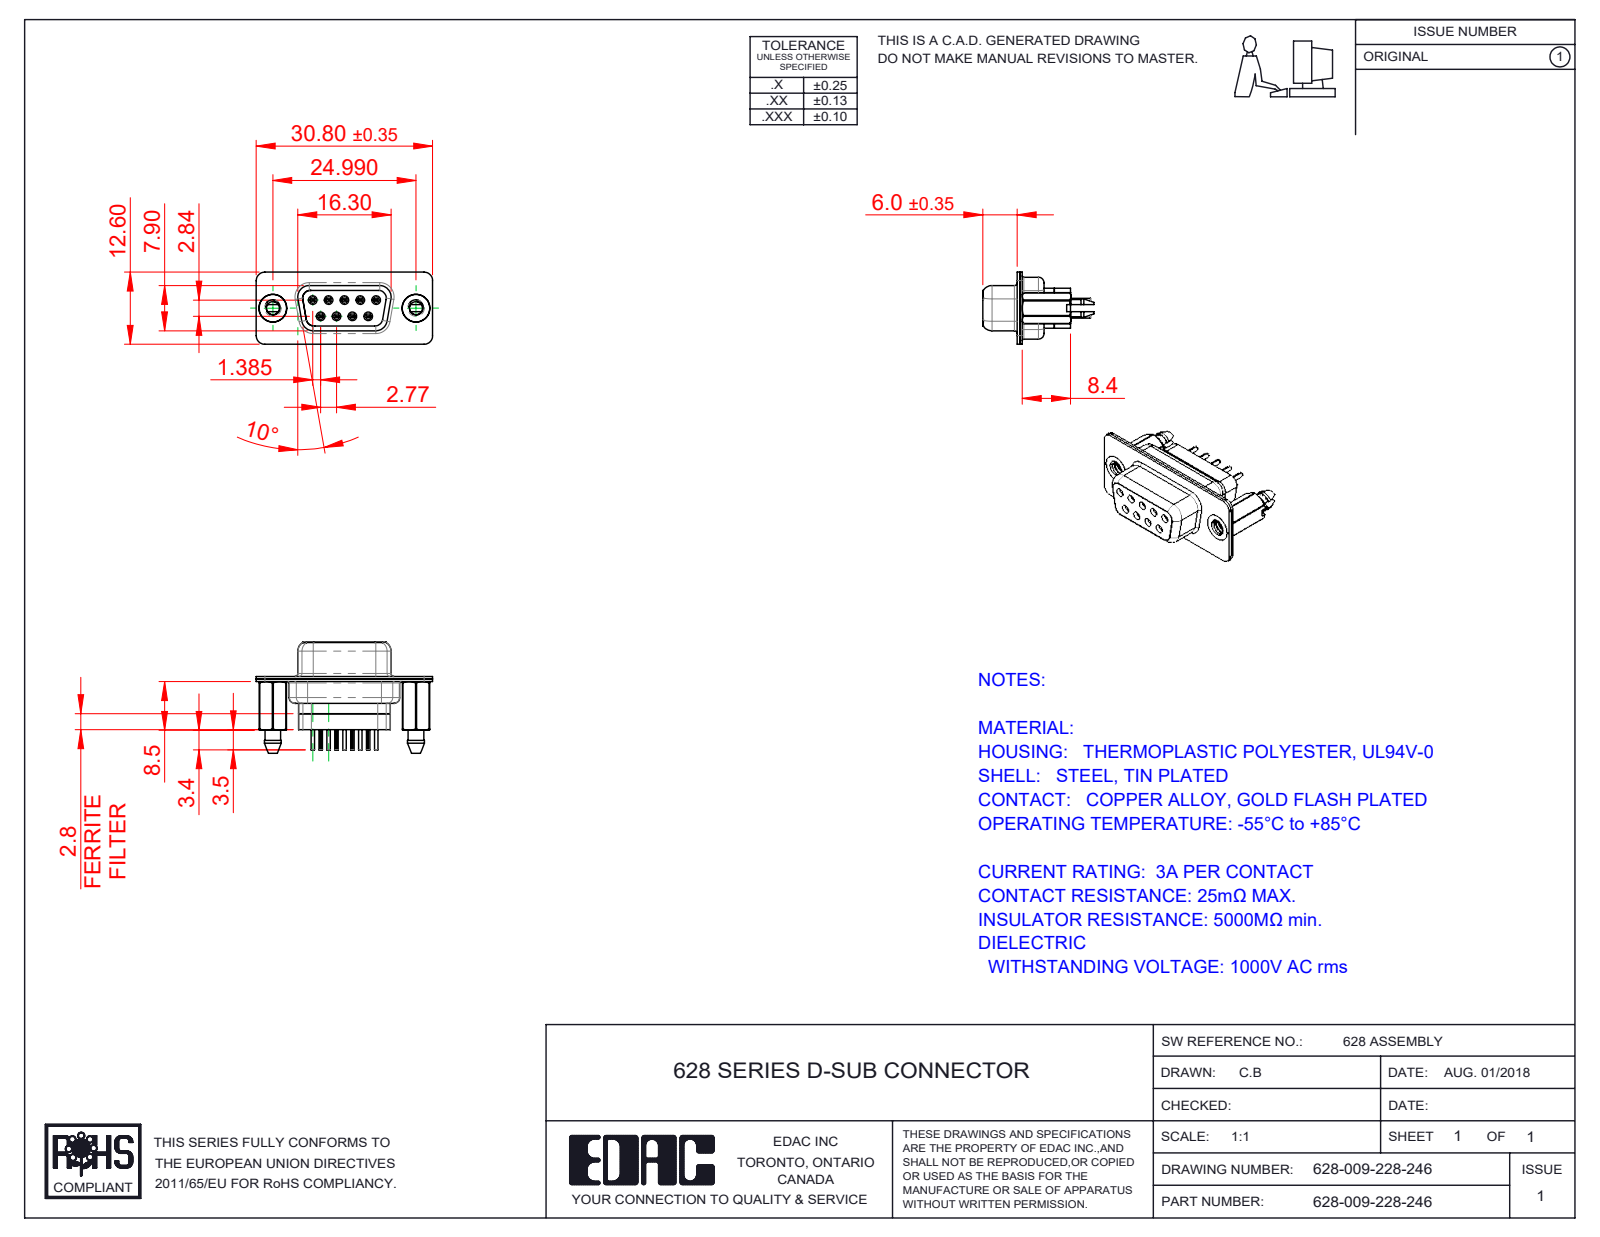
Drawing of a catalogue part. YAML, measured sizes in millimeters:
part_name: "628 4-40 Threaded Boardlock_FF; 628 Shell Front_09 Contacts; 628 Housing_09 FF; 628-009-228-246 (+3 more)"
step_written_by: "SolidWorks 2020 (CONFIG_CONTROL_DESIGN)"
units: millimeters
bodies: {solids: 15, faces: 1607, planar: 384, cylindrical: 523, other: 700}
overall_size: [30.8, 19.4, 12.6]
volume: 2184
surface_area: 5433
round_holes:
  - {diameter: 0.2, count: 9}
  - {diameter: 0.8, count: 9}
  - {diameter: 0.9, count: 9}
  - {diameter: 1.1, count: 9}
  - {diameter: 1.6, count: 9}
  - {diameter: 1.7, count: 5}
  - {diameter: 2.26, count: 2}
  - {diameter: 4, count: 2}
  - {diameter: 4.05, count: 2}
  - {diameter: 4.85, count: 2}
round_bosses_or_shafts:
  - {diameter: 2, count: 9}
  - {diameter: 1.5, count: 9}
  - {diameter: 1.2, count: 9}
  - {diameter: 0.6, count: 9}
  - {diameter: 4.95, count: 2}
  - {diameter: 4.8, count: 2}
partial_cylinders:
  - {radius: 1.5, count: 19}
  - {radius: 0.1, count: 18}
  - {radius: 2, count: 12}
  - {radius: 0.28, count: 9}
  - {radius: 1.35, count: 6}
  - {radius: 1.6, count: 6}
  - {radius: 0.25, count: 4}
  - {radius: 0.5, count: 4}
face_to_face_distances: [0.45, 0.4, 0.9, 6.05, 6.5, 8.85, 8.5, 5.6, 6.6, 8.4]
hole_center_spacings: [3.16, 2.77, 5.54, 5.03, 5.04, 8.31, 7.48, 7.49]
